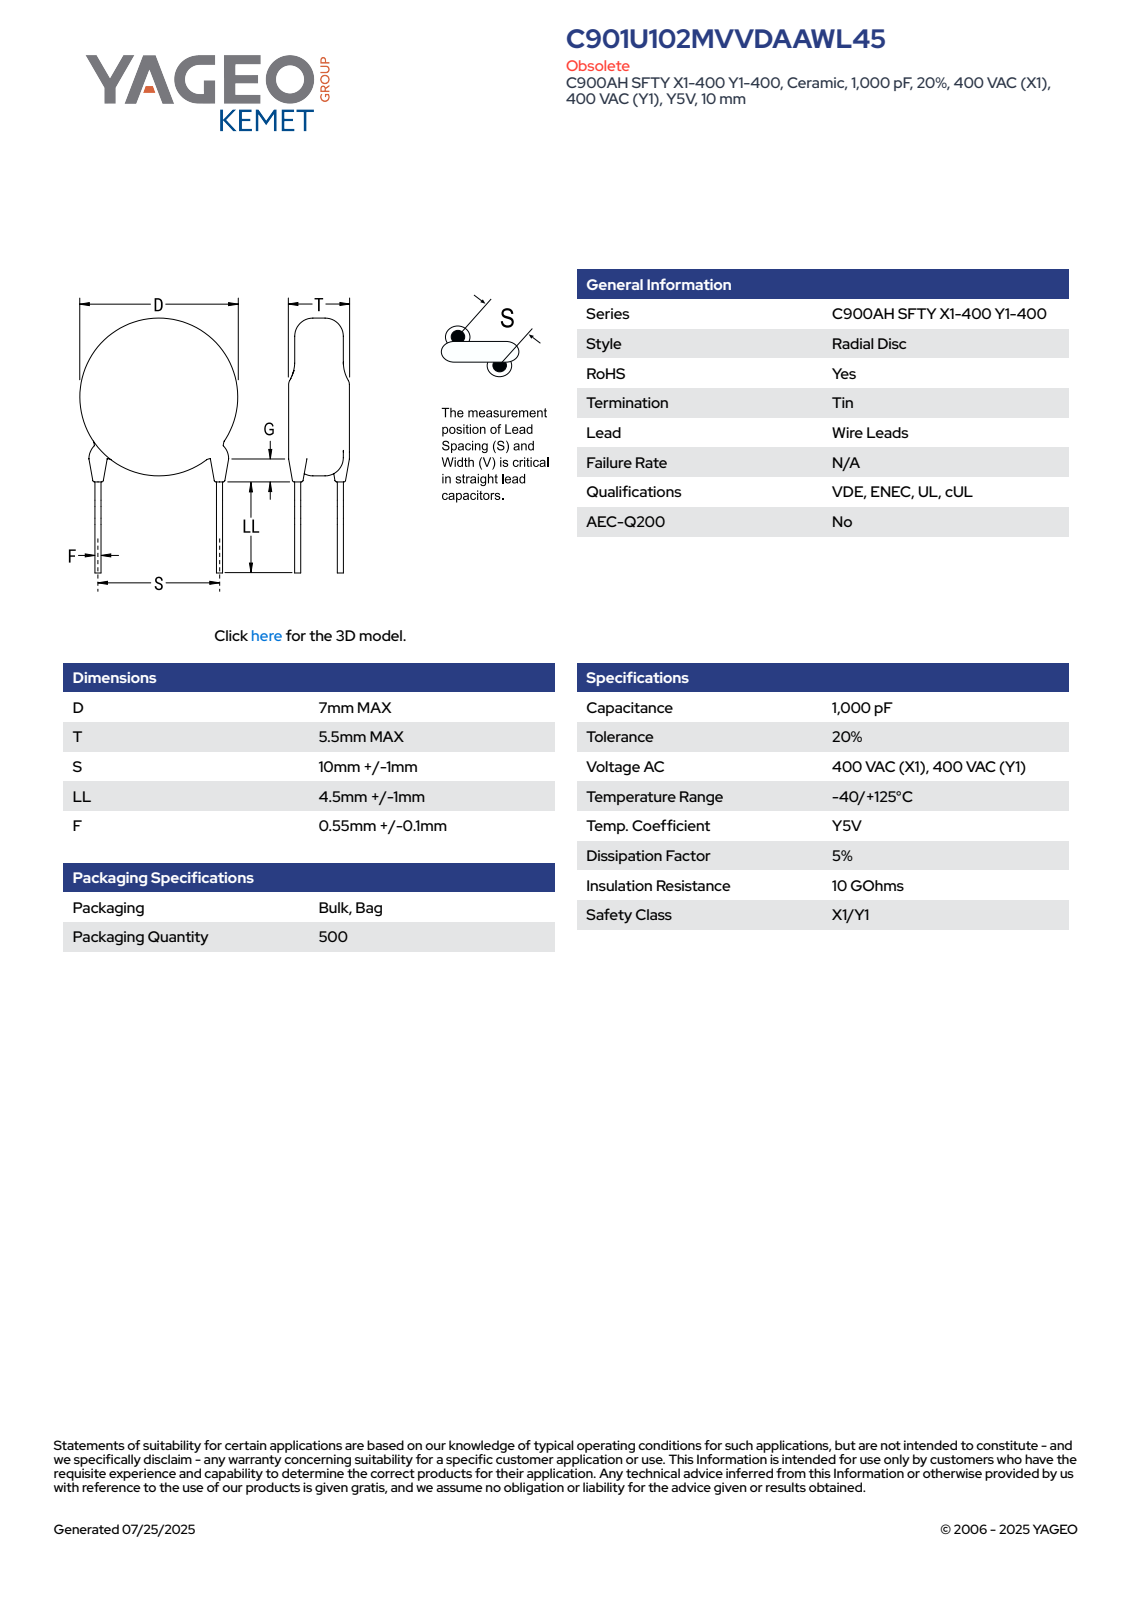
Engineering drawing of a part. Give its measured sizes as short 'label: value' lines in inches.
name: CCD_STC900_D7T5.5S10LL5.5F0.65G3
written by: SolidWorks 2014 (AUTOMOTIVE_DESIGN)
unit: in
bodies: 4 solids, 83 faces (61 planar, 6 cylindrical, 16 other)
size: 0.509 × 0.385 × 0.217
volume: 0.013 in³; area: 0.343 in²
bosses: 2× ⌀0.026, 1× ⌀0.276
face distances: 0.217, 0.032, 0.387, 0.356, 0.13, 0.066, 0.139, 0.094, 0.098, 0.052
